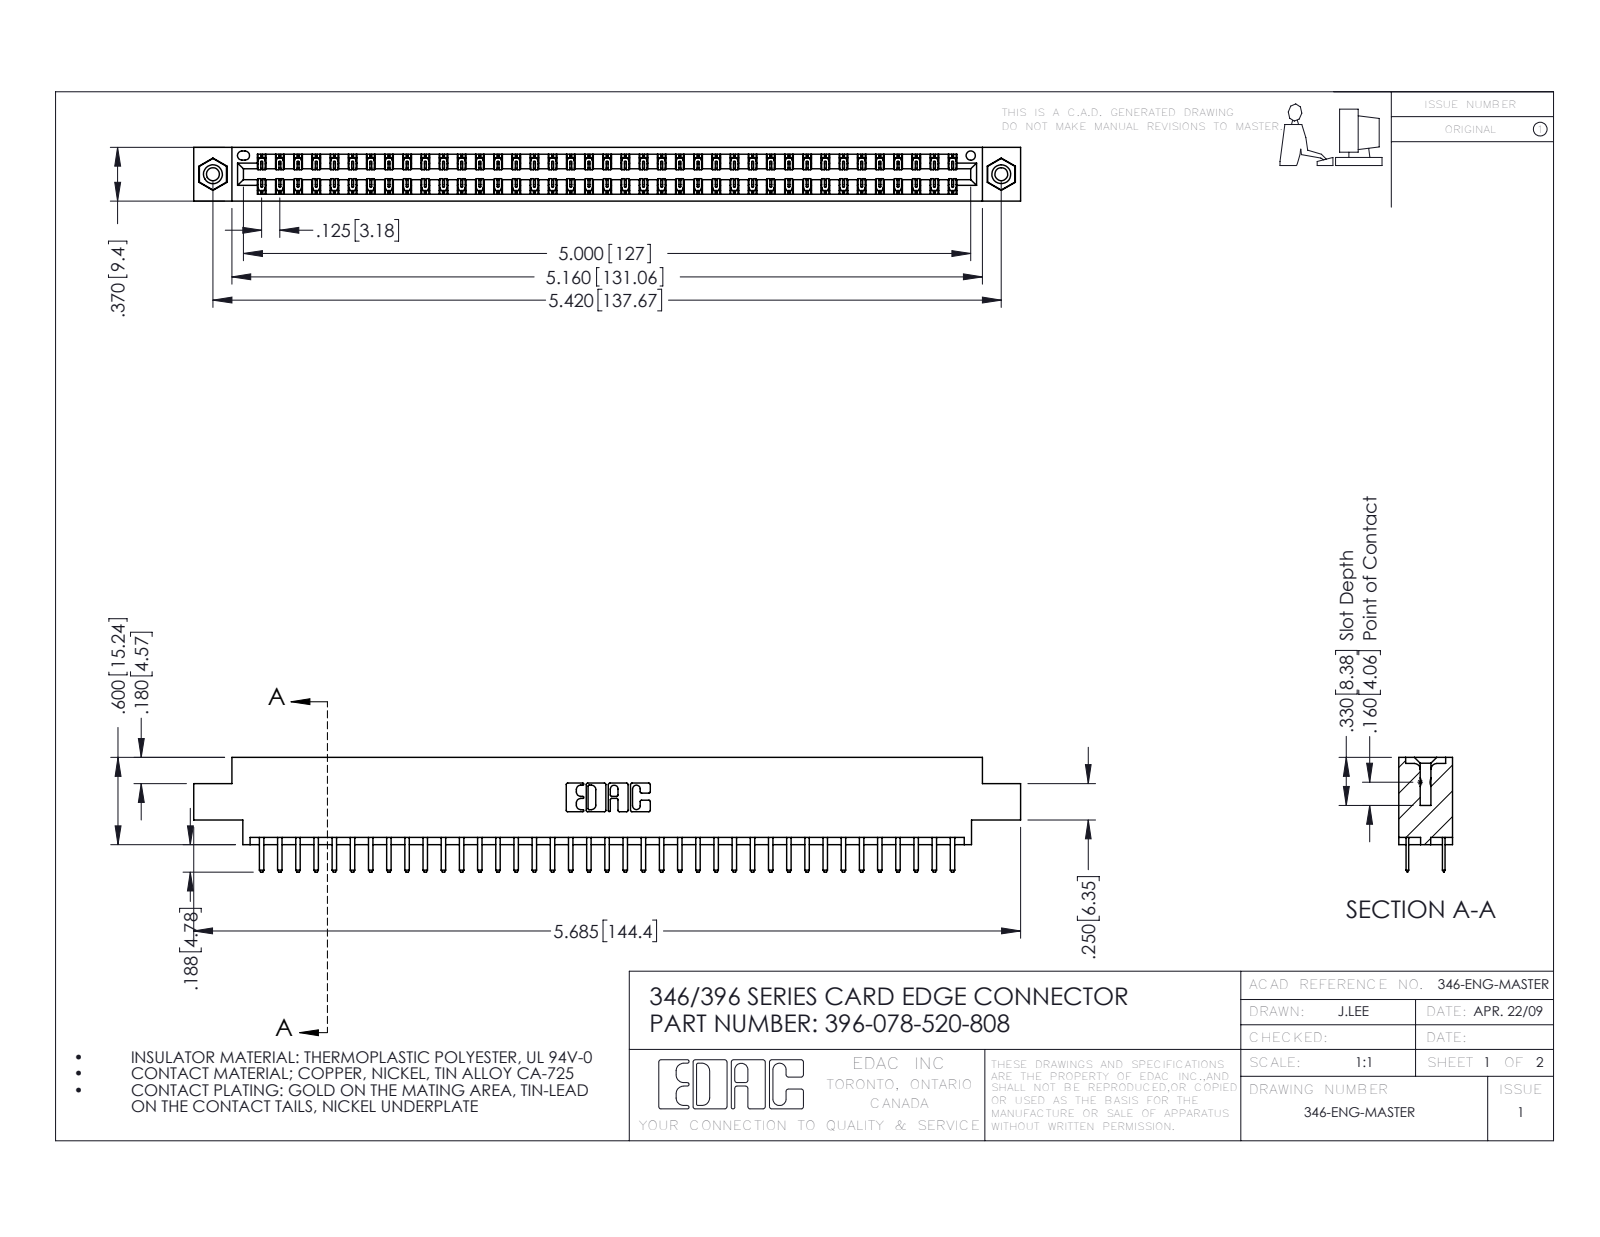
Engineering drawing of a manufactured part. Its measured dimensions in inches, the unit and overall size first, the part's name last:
Units: inches
Overall size (bounding box): 5.685 × 0.788 × 0.37
Round holes (diameter × count): ⌀0.089 ×2, ⌀0.125 ×2, ⌀0.156 ×2, ⌀0.064 ×1
Round bosses / shafts (diameter × count): ⌀0.155 ×2
Partial cylindrical surfaces — rounded edges, fillets, slot ends (radius × count): R0.006 ×117, R0.01 ×82, R0.01 ×22, R0.007 ×6, R0.031 ×6, R0.026 ×3, R0.014 ×2, R0.022 ×2
Main face-to-face distances: 0.048, 0.322, 0.25, 0.37, 0.275, 0.072, 0.298, 0.025, 0.222, 0.148
Hole centre spacings: 0.246, 5.211, 5.42
Volume: 0.846 in³ · Surface area: 29.65 in²
Bodies: 81 solids, 4554 faces (2998 planar, 1540 cylindrical, 16 other)
Part name (STEP PRODUCT): 396-078-520-808; 345-250-001_345-250-003-102; 346 Part_0.170 Offset - 0.156 Dia-TI; 345-292-001_345-293-120
STEP written by: SolidWorks 2016 (CONFIG_CONTROL_DESIGN)
